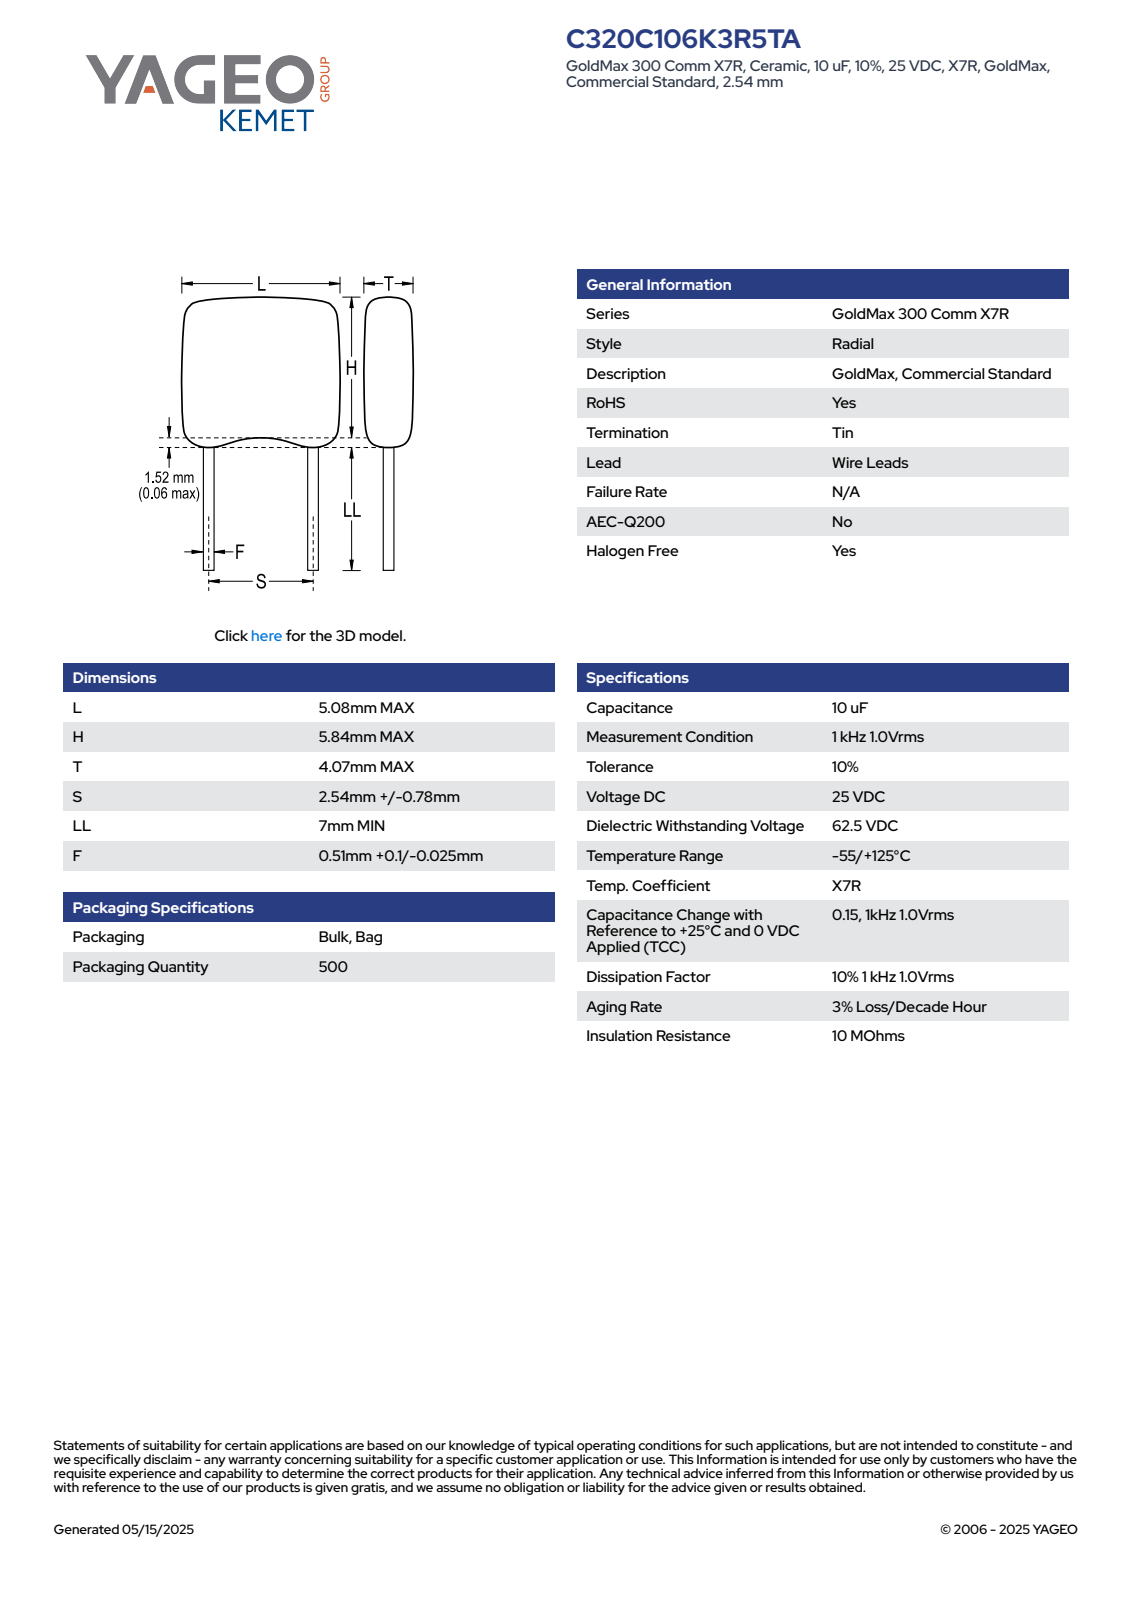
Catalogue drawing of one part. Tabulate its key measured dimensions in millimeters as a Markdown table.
| quantity | value |
| --- | --- |
| part name | CCR_KRCST_C320_L5.08H5.84T4.07S2.54LL7F0.61 |
| STEP written by | SolidWorks 2014 (AUTOMOTIVE_DESIGN) |
| units | millimeters |
| bodies | 4 solids, 83 faces (65 planar, 14 cylindrical, 4 other) |
| overall size | 14.36 × 5.08 × 4.08 |
| volume | 150 mm³ |
| surface area | 185 mm² |
| round bosses / shafts (diameter × count) | 0.61 × 2 |
| partial cylindrical surfaces (radius × count) | 0.75 × 10 |
| main face-to-face distances | 4.07, 5.08, 7.36, 7, 14.36, 4.08, 0.54, 10.98, 3.98, 3.38 |
